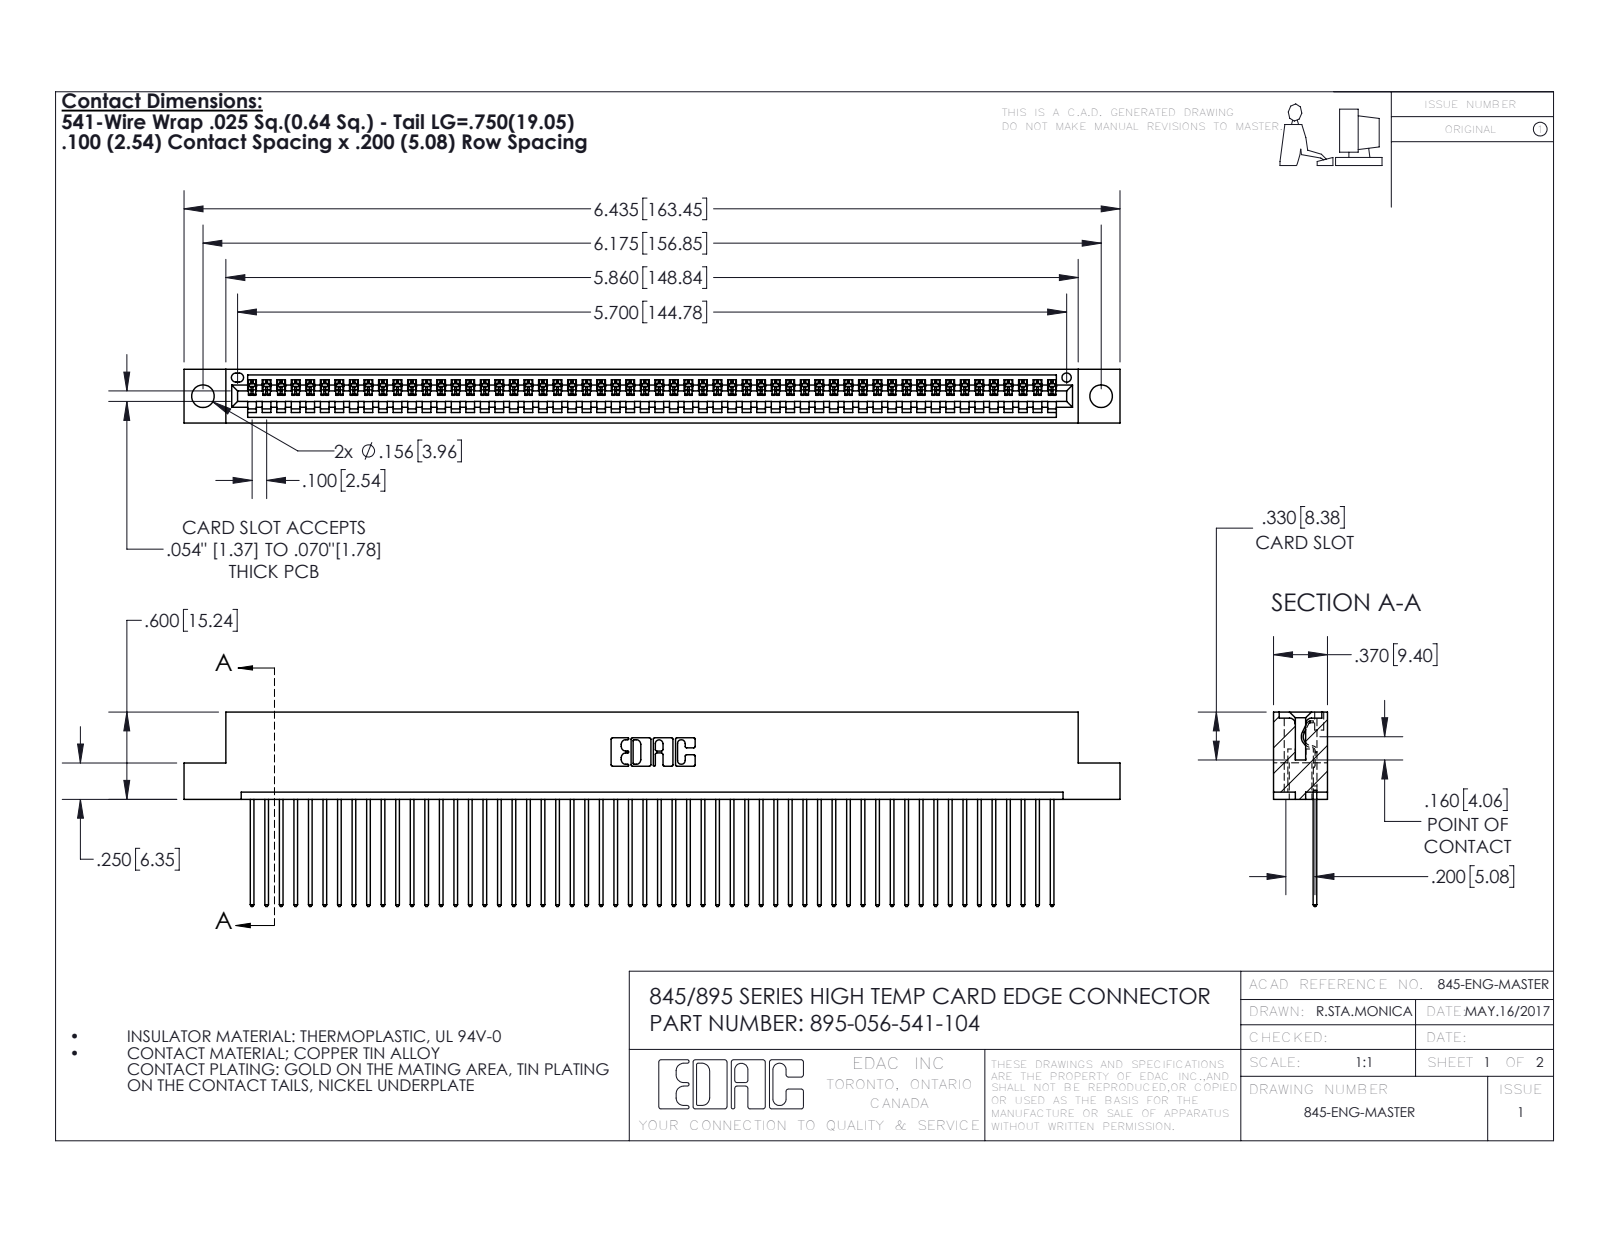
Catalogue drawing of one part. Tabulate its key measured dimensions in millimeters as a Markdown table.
| quantity | value |
| --- | --- |
| part name | 345 Part_Flush Mounting Lugs - 0.156 Dia-TH; 395-056-541-104; 345-292-001_345-293-141 |
| STEP written by | SolidWorks 2016 (CONFIG_CONTROL_DESIGN) |
| units | millimeters |
| bodies | 57 solids, 3374 faces (2320 planar, 1054 cylindrical, 0 other) |
| overall size | 163.4 × 34 × 9.4 |
| volume | 15 700 mm³ |
| surface area | 22 000 mm² |
| round holes (diameter × count) | 4 × 2, 1.6 × 1 |
| partial cylindrical surfaces (radius × count) | 0.2 × 112, 0.3 × 112, 0.3 × 22, 0.2 × 6, 0.8 × 6, 0.7 × 3, 0.8 × 2, 1 × 2 |
| main face-to-face distances | 1.8, 7.6, 2.5, 6.9, 0.6, 9.4, 5.1, 5.7, 3.8, 1.8 |
| hole center spacings | 6.9, 150.9, 156.8 |
